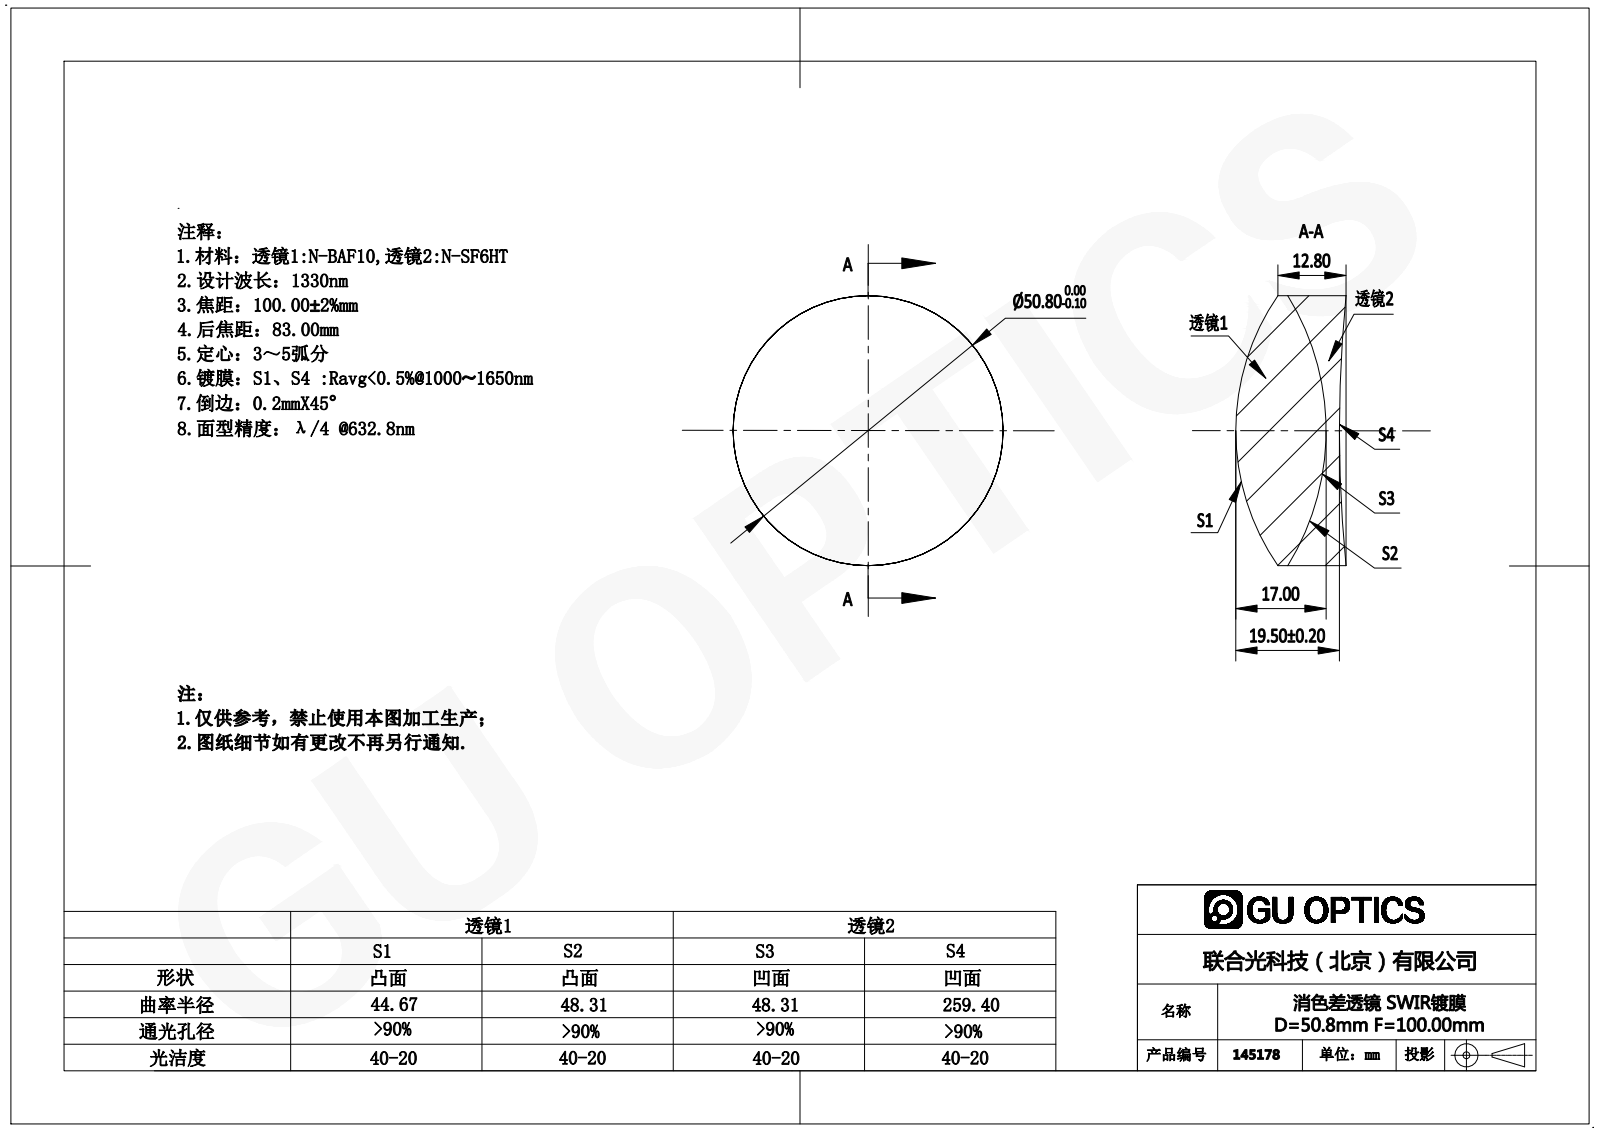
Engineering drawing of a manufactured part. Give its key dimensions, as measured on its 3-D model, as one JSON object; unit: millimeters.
{"part_name": "145178", "step_written_by": "SolidWorks 2016 (AUTOMOTIVE_DESIGN)", "units": "millimeters", "bodies": {"solids": 2, "faces": 12, "planar": 0, "cylindrical": 4, "other": 8}, "overall_size": [50.8, 50.8, 20.75], "volume_mm3": 33015, "surface_area_mm2": 10683, "round_bosses_or_shafts": [[50.8, 1]]}
